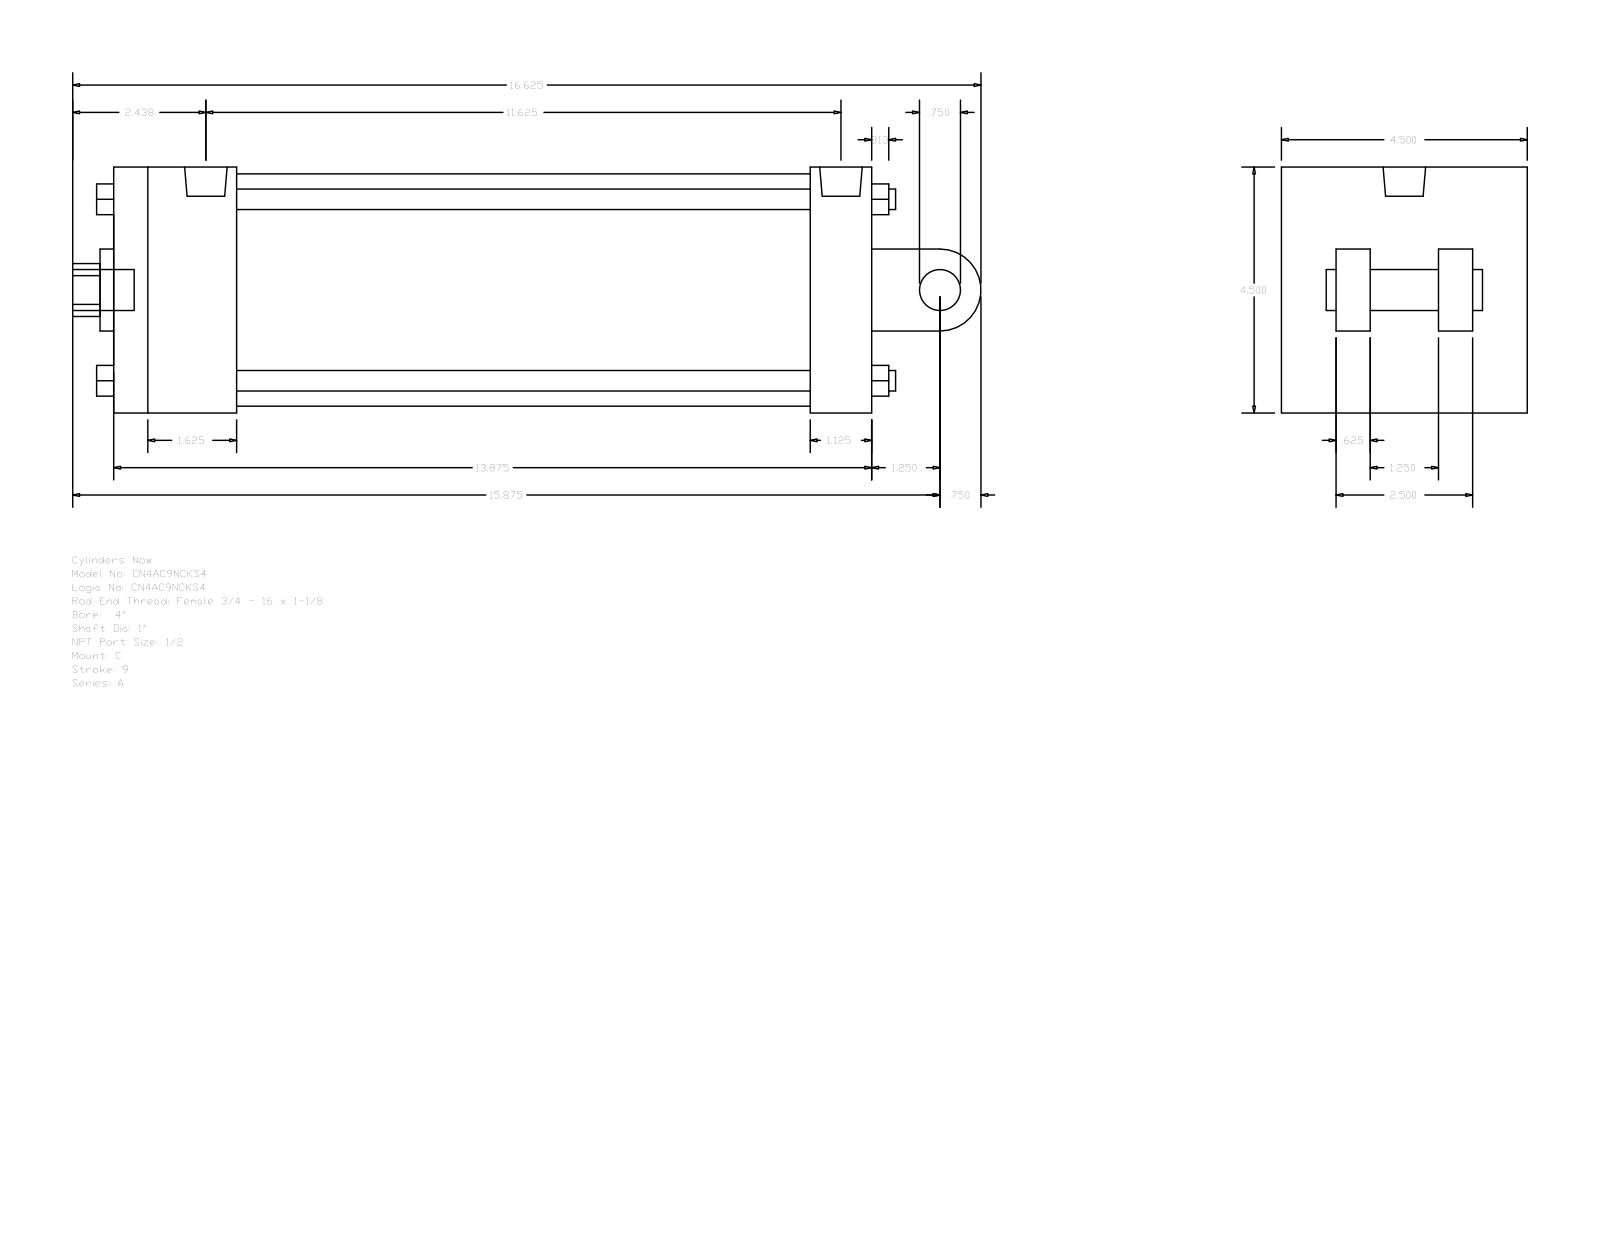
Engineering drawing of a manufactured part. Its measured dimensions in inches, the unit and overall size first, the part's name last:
Units: inches
Overall size (bounding box): 16.625 × 4.5 × 4.5
Round holes (diameter × count): ⌀0.344 ×2, ⌀0.778 ×1, ⌀1 ×1, ⌀1.5 ×1, ⌀4.25 ×1
Round bosses / shafts (diameter × count): ⌀0.375 ×4, ⌀0.75 ×2, ⌀0.344 ×2, ⌀0.778 ×1
Partial cylindrical surfaces — rounded edges, fillets, slot ends (radius × count): R0.484 ×1, R0.75 ×1
Main face-to-face distances: 4.5, 13.875, 2.875, 12.75, 1.125, 2.25, 10.5, 11.625, 0.625, 1.875
Hole centre spacings: 0.125
Bodies: 0 solids, 135 faces (102 planar, 33 cylindrical, 0 other)
Part name (STEP PRODUCT): A_C__0400_1
STEP written by: GSSL Pune (CONFIG_CONTROL_DESIGN)
